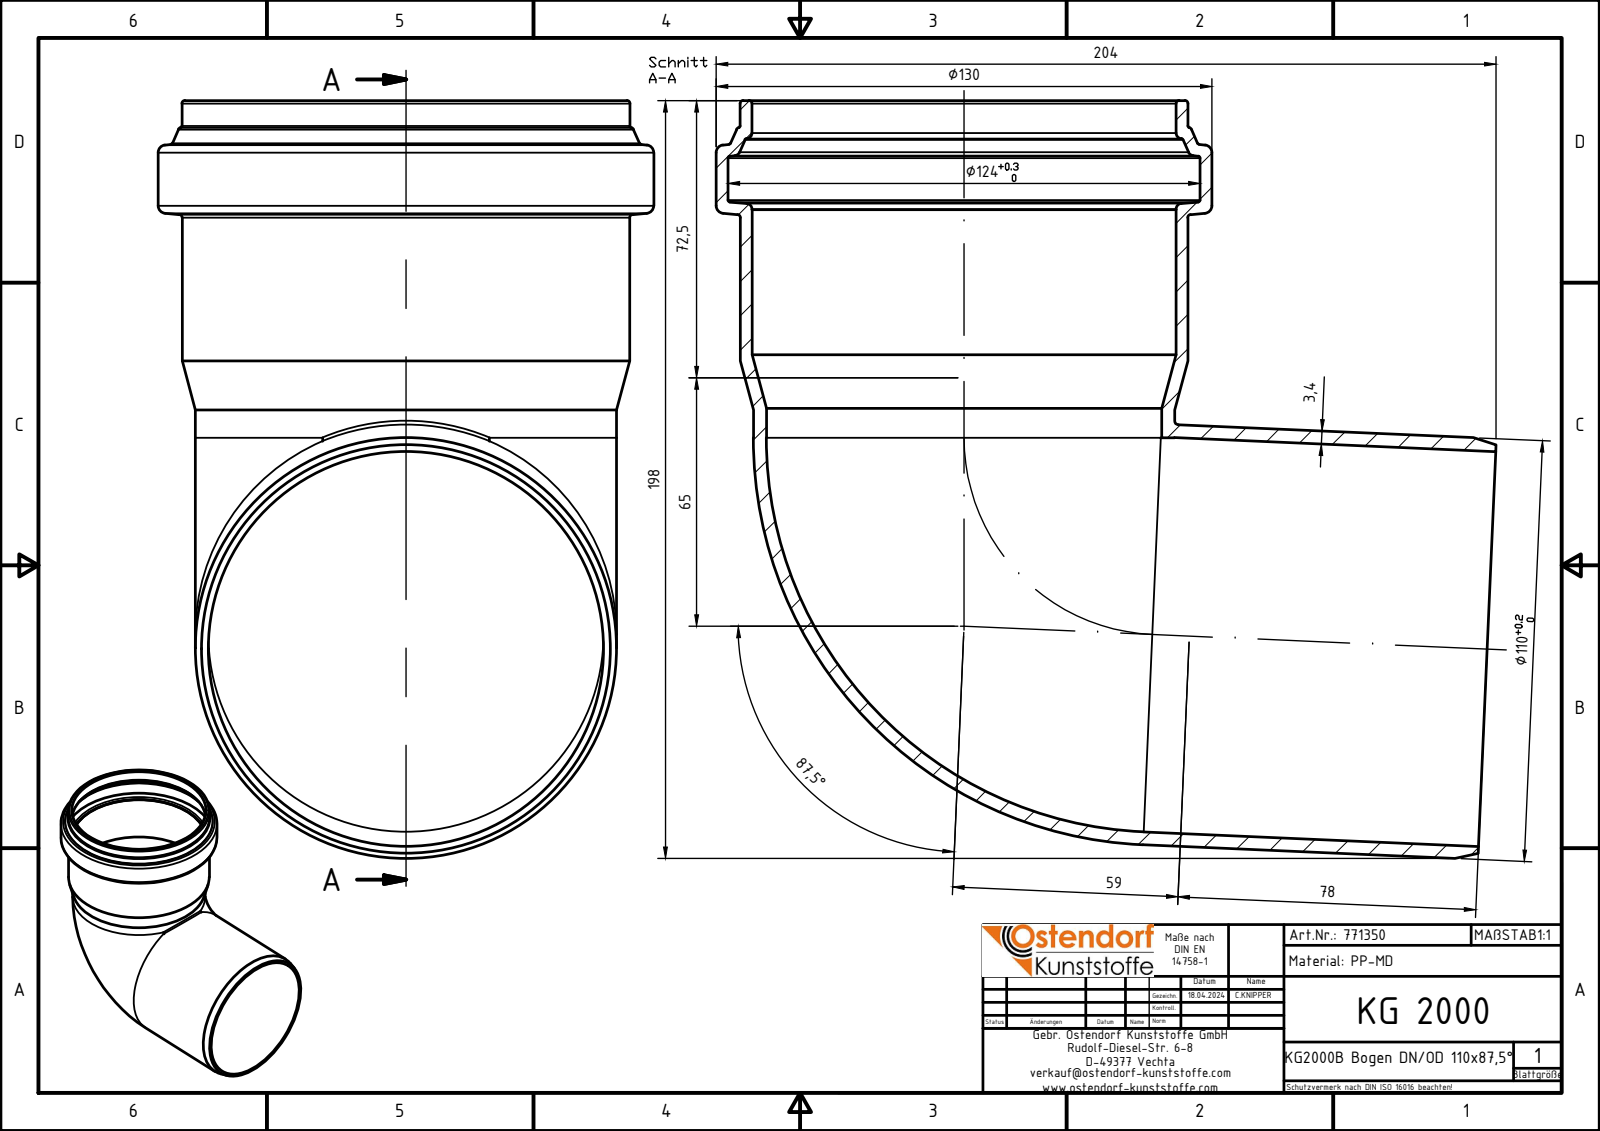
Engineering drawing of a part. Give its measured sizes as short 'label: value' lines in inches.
name: 771350z
written by: Autodesk Inventor 2024 (AUTOMOTIVE_DESIGN)
unit: in
bodies: 1 solid, 43 faces (4 planar, 12 cylindrical, 27 other)
size: 8.033 × 7.806 × 5.106
volume: 16.96 in³; area: 284.7 in²
holes: 2× ⌀4.071, 1× ⌀4.366, 1× ⌀4.37, 1× ⌀4.862
bosses: 2× ⌀4.339, 1× ⌀5.106, 1× ⌀4.614, 1× ⌀4.61
face distances: 3.472, 2.35, 1.122
